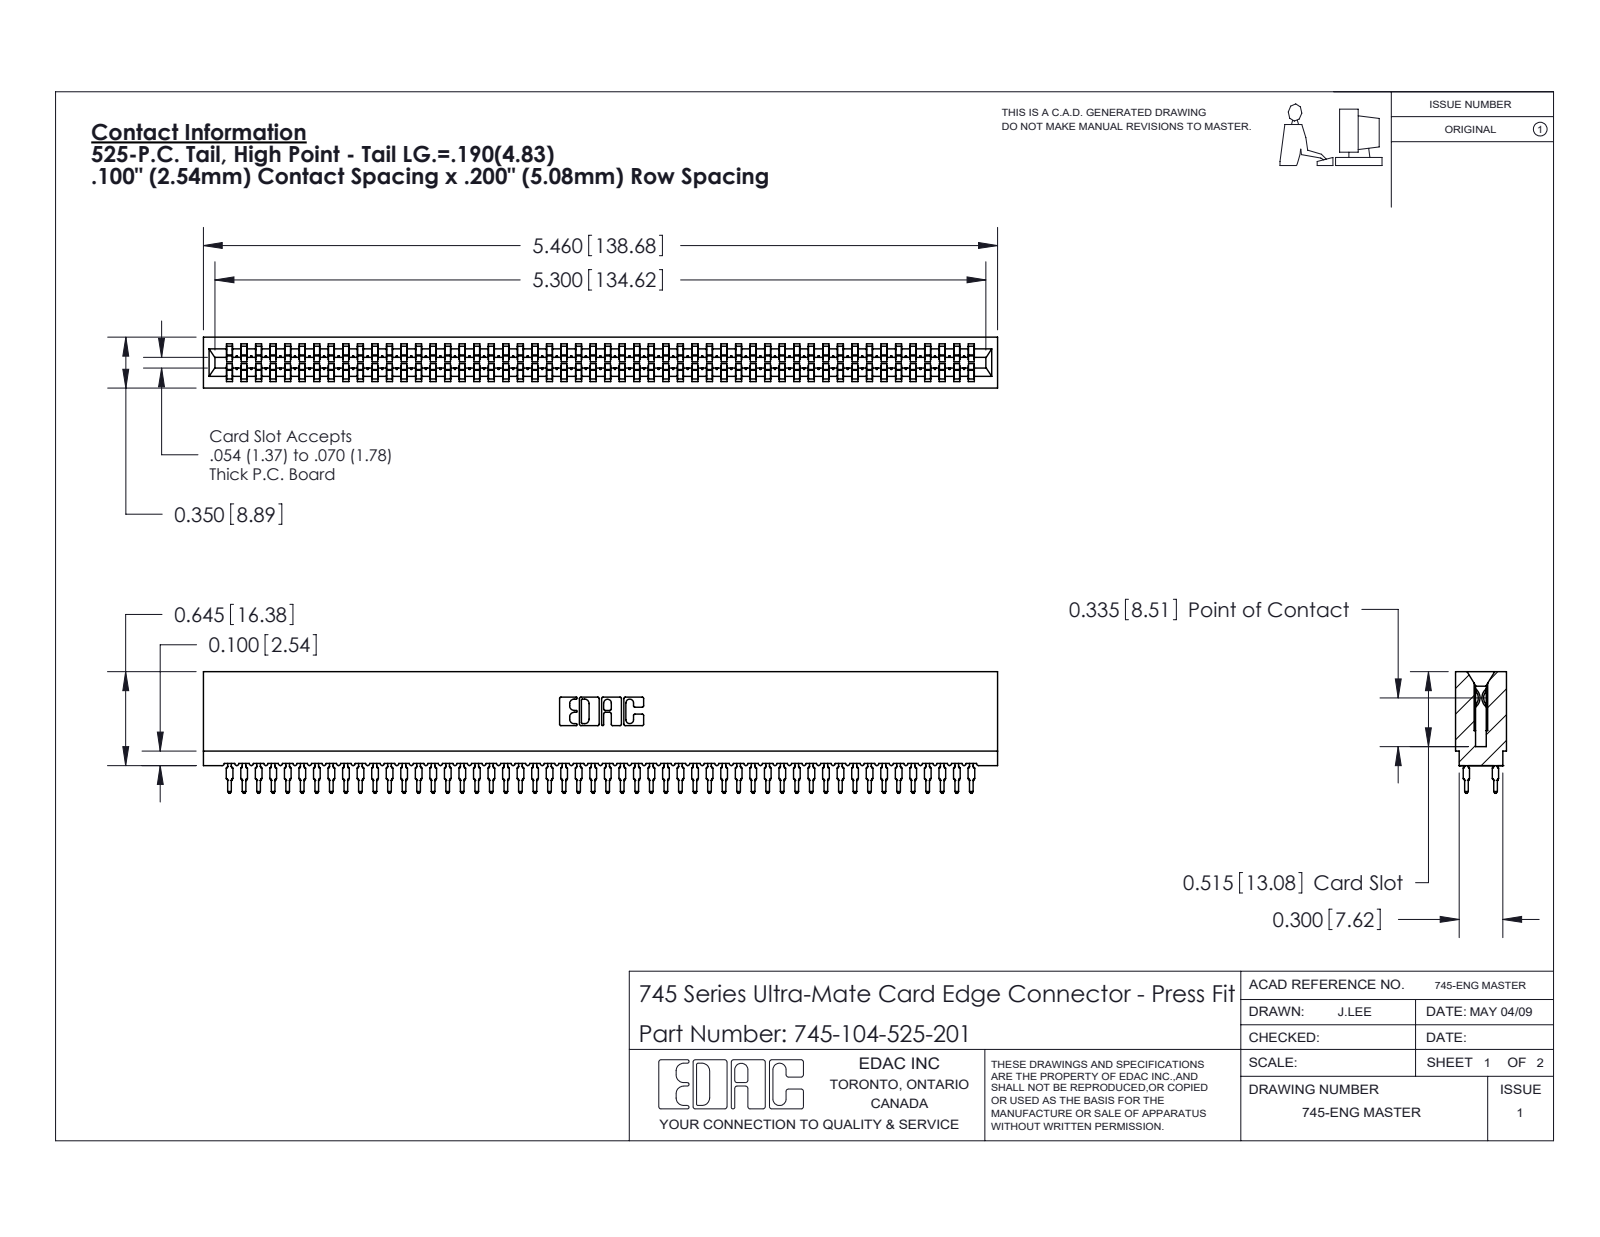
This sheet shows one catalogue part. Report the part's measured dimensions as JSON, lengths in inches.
{"part_name": "745-292-001_525; 745-104-525-201; 745 Part_Insulator Option - 01", "step_written_by": "SolidWorks 2020 (CONFIG_CONTROL_DESIGN)", "units": "inches", "bodies": {"solids": 105, "faces": 9403, "planar": 4839, "cylindrical": 1860, "other": 2704}, "overall_size": [5.46, 0.836, 0.35], "volume_in3": 0.757, "surface_area_in2": 39.29, "partial_cylinders_radius": [[0.021, 208], [0.015, 104], [0.01, 22], [0.005, 8], [0.011, 8], [0.007, 6], [0.031, 6], [0.026, 3]], "face_to_face_distances": [0.35, 0.063, 0.287, 0.045, 0.305, 0.018, 0.243, 0.138, 0.212, 0.093]}
